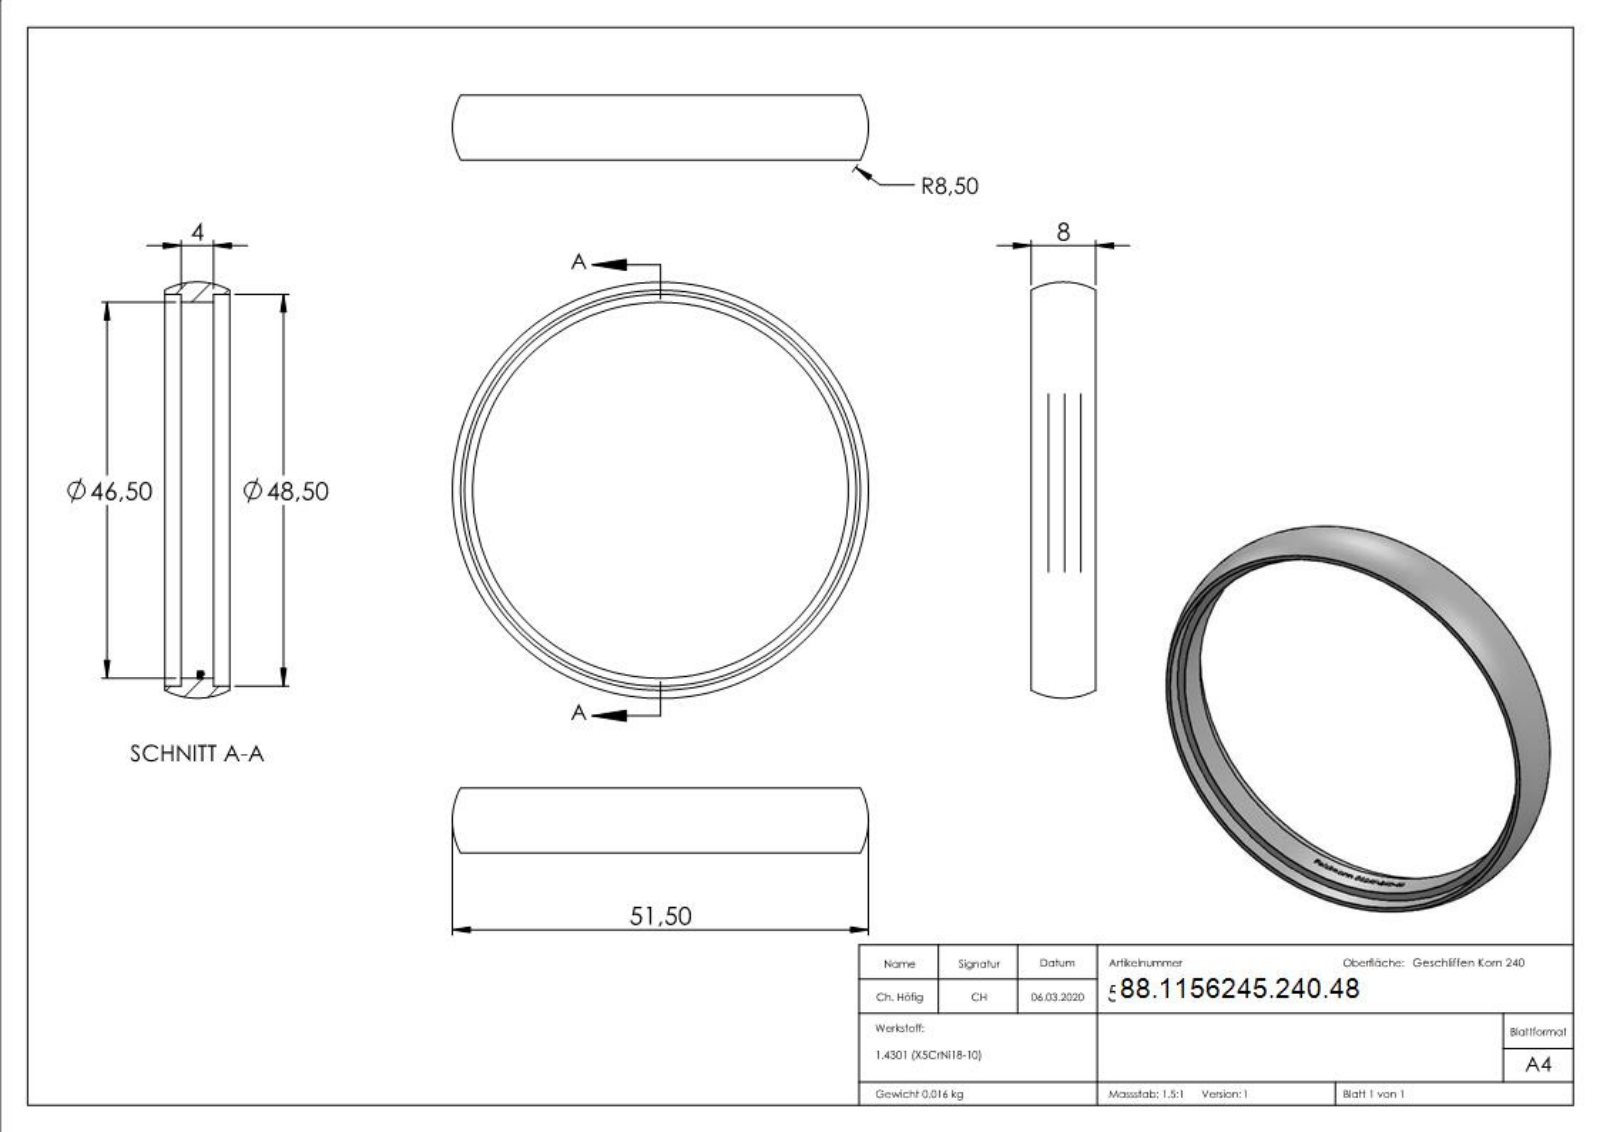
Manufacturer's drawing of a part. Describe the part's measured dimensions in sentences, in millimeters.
The part is named "56245-240-48". Its 3-D file was written by "SolidWorks 2015 (CONFIG_CONTROL_DESIGN)". It is 1 solid with 277 faces: 132 planar, 33 cylindrical and 112 other. Overall it measures 51.5 by 51.5 by 8 millimeters. Its volume is 2 066 cubic millimeters and its surface area 2 983 square millimeters. Round holes: 1 of diameter 46.5, 1 of diameter 48.5. Partial cylindrical surfaces (rounded edges, fillets, slot ends): 1 of radius 23.35. The main face-to-face distances are 2, 6, 4, 8, 1.21, 2.2, 3.74, 1.78, 7.78, 1.74.
